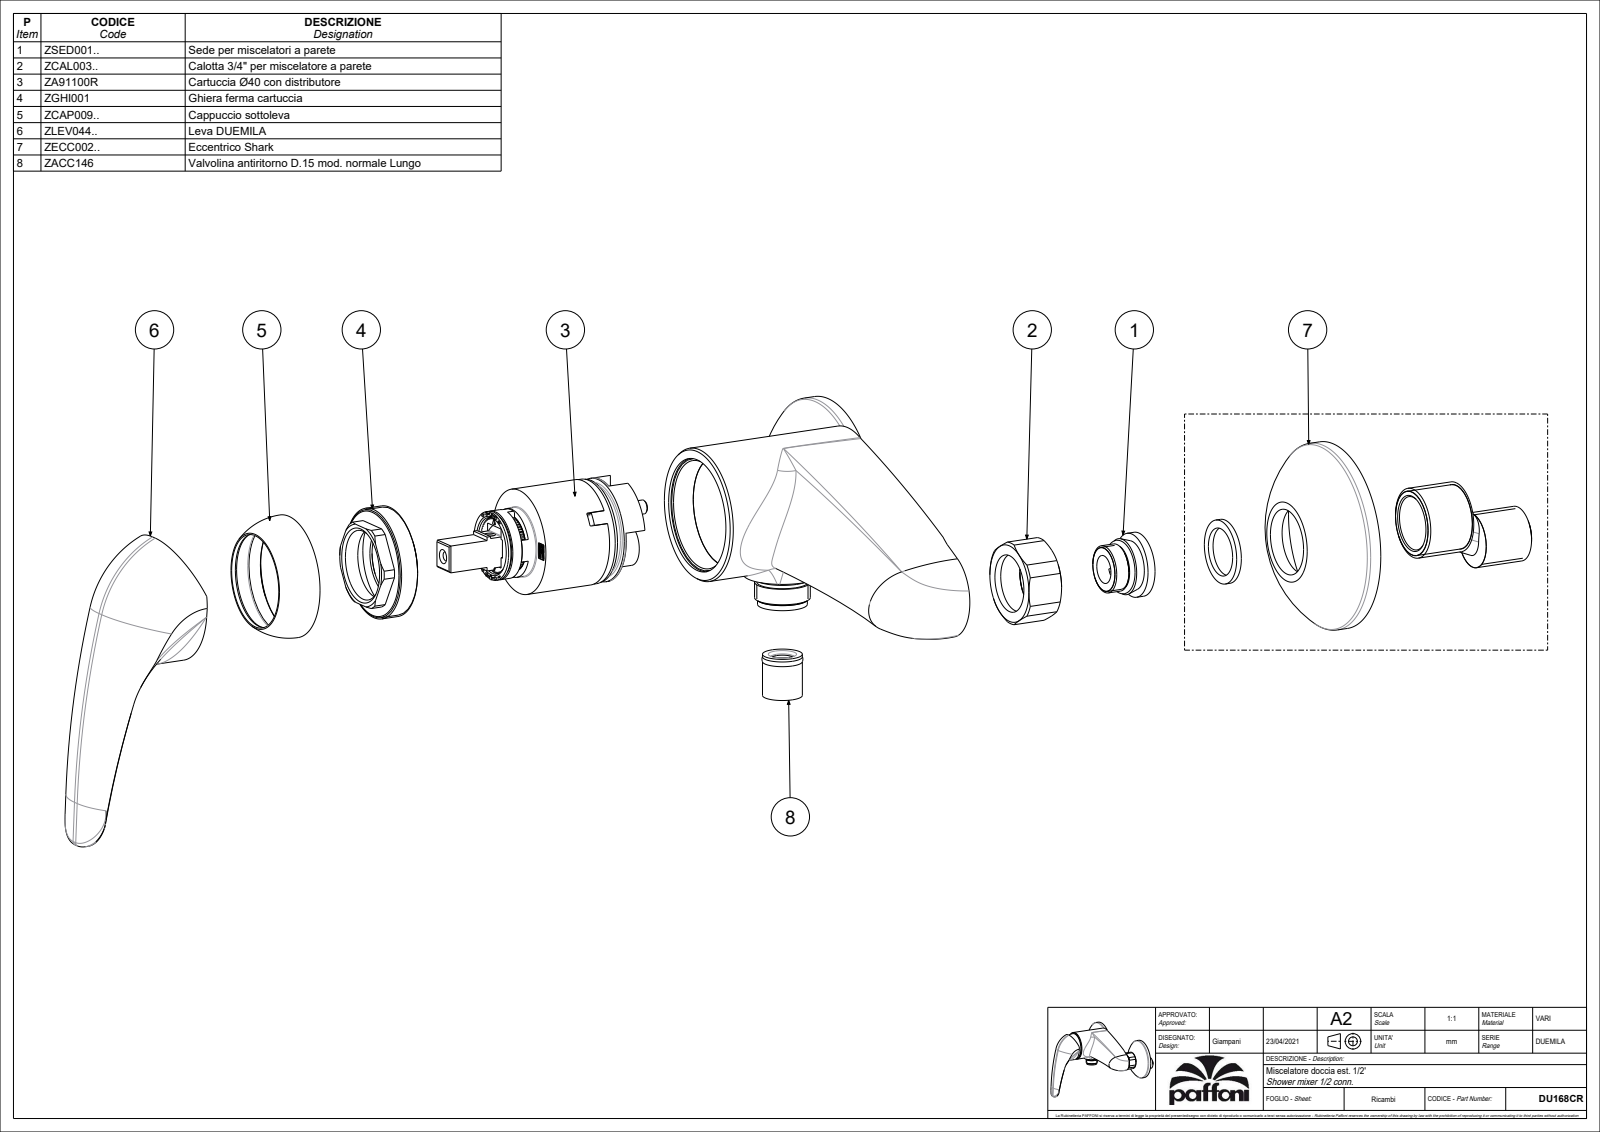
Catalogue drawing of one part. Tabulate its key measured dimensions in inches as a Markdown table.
| quantity | value |
| --- | --- |
| part name | DU168CR |
| STEP written by | CREO PARAMETRIC BY PTC INC, 2020044 (CONFIG_CONTROL_DESIGN) |
| units | inches |
| bodies | 1 solid, 189 faces (36 planar, 43 cylindrical, 110 other) |
| overall size | 8.661 × 5.769 × 4.581 |
| volume | 30.56 in³ |
| surface area | 105 in² |
| round holes (diameter × count) | 0.362 × 1 |
| round bosses / shafts (diameter × count) | 2.756 × 2, 1.969 × 1, 0.815 × 1, 0.728 × 1, 0.713 × 1, 0.197 × 1 |
| partial cylindrical surfaces (radius × count) | 0.059 × 2, 0.591 × 2, 0.61 × 2, 0.807 × 2, 0.945 × 2, 0.965 × 2, 0.709 × 1, 1.537 × 1 |
| main face-to-face distances | 1.378, 1.398, 0.02, 4.488, 3.11, 3.091, 1.339, 0.039, 0.059, 3.15 |
